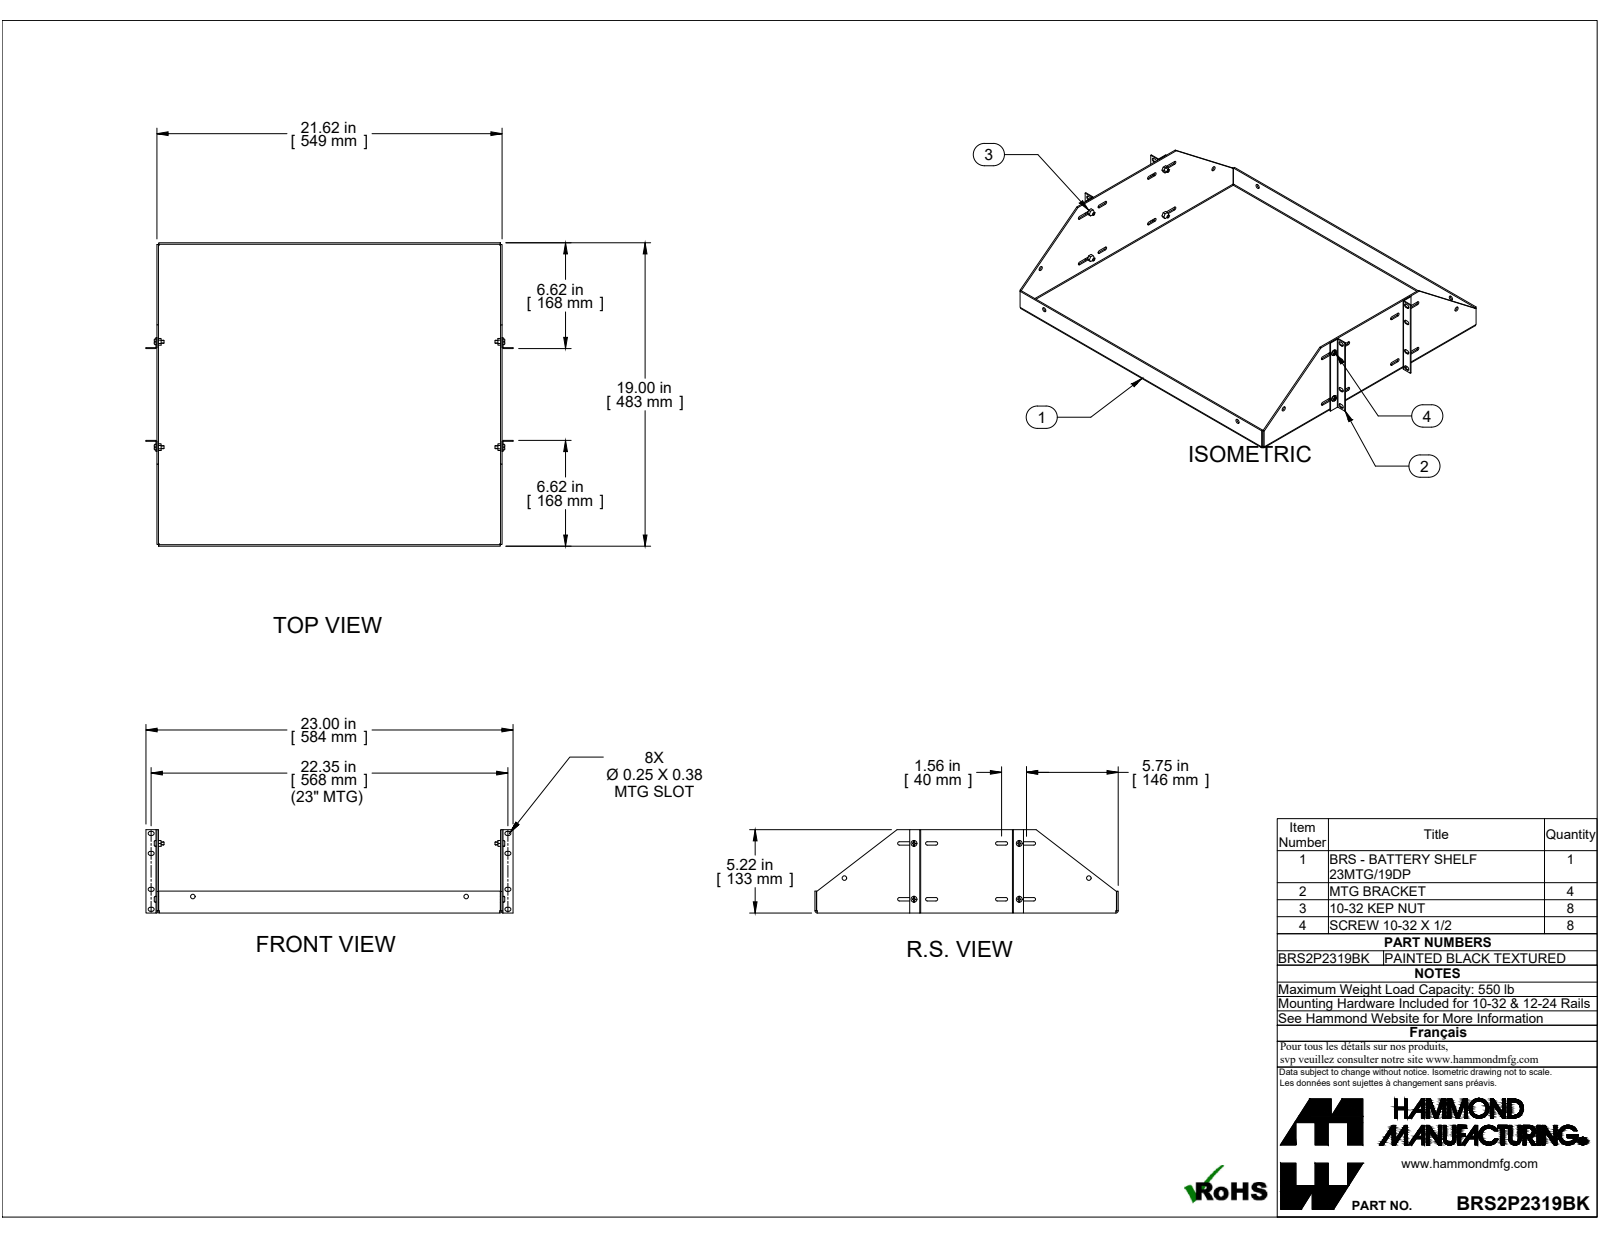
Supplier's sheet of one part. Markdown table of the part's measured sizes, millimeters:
| quantity | value |
| --- | --- |
| part name | BRS2P2319BK |
| STEP written by | SolidWorks 2019 (CONFIG_CONTROL_DESIGN) |
| units | millimeters |
| bodies | 21 solids, 466 faces (322 planar, 120 cylindrical, 24 other) |
| overall size | 584.2 × 482.6 × 132.5 |
| volume | 981 900 mm³ |
| surface area | 840 000 mm² |
| round holes (diameter × count) | 4 × 4, 5.4 × 4, 7.1 × 4 |
| round bosses / shafts (diameter × count) | 9.4 × 4, 4.8 × 4 |
| partial cylindrical surfaces (radius × count) | 3.2 × 16, 2.7 × 12, 0.7 × 4, 1.2 × 4, 2.2 × 4, 3.6 × 4 |
| main face-to-face distances | 2.4, 546.9, 2.4, 549.3, 544.4, 480.2, 477.8, 482.6, 1.4, 3.9 |
| hole center spacings | 88.9, 115.7, 123.7, 167.6, 189.7, 280.3, 283.7, 389 |
